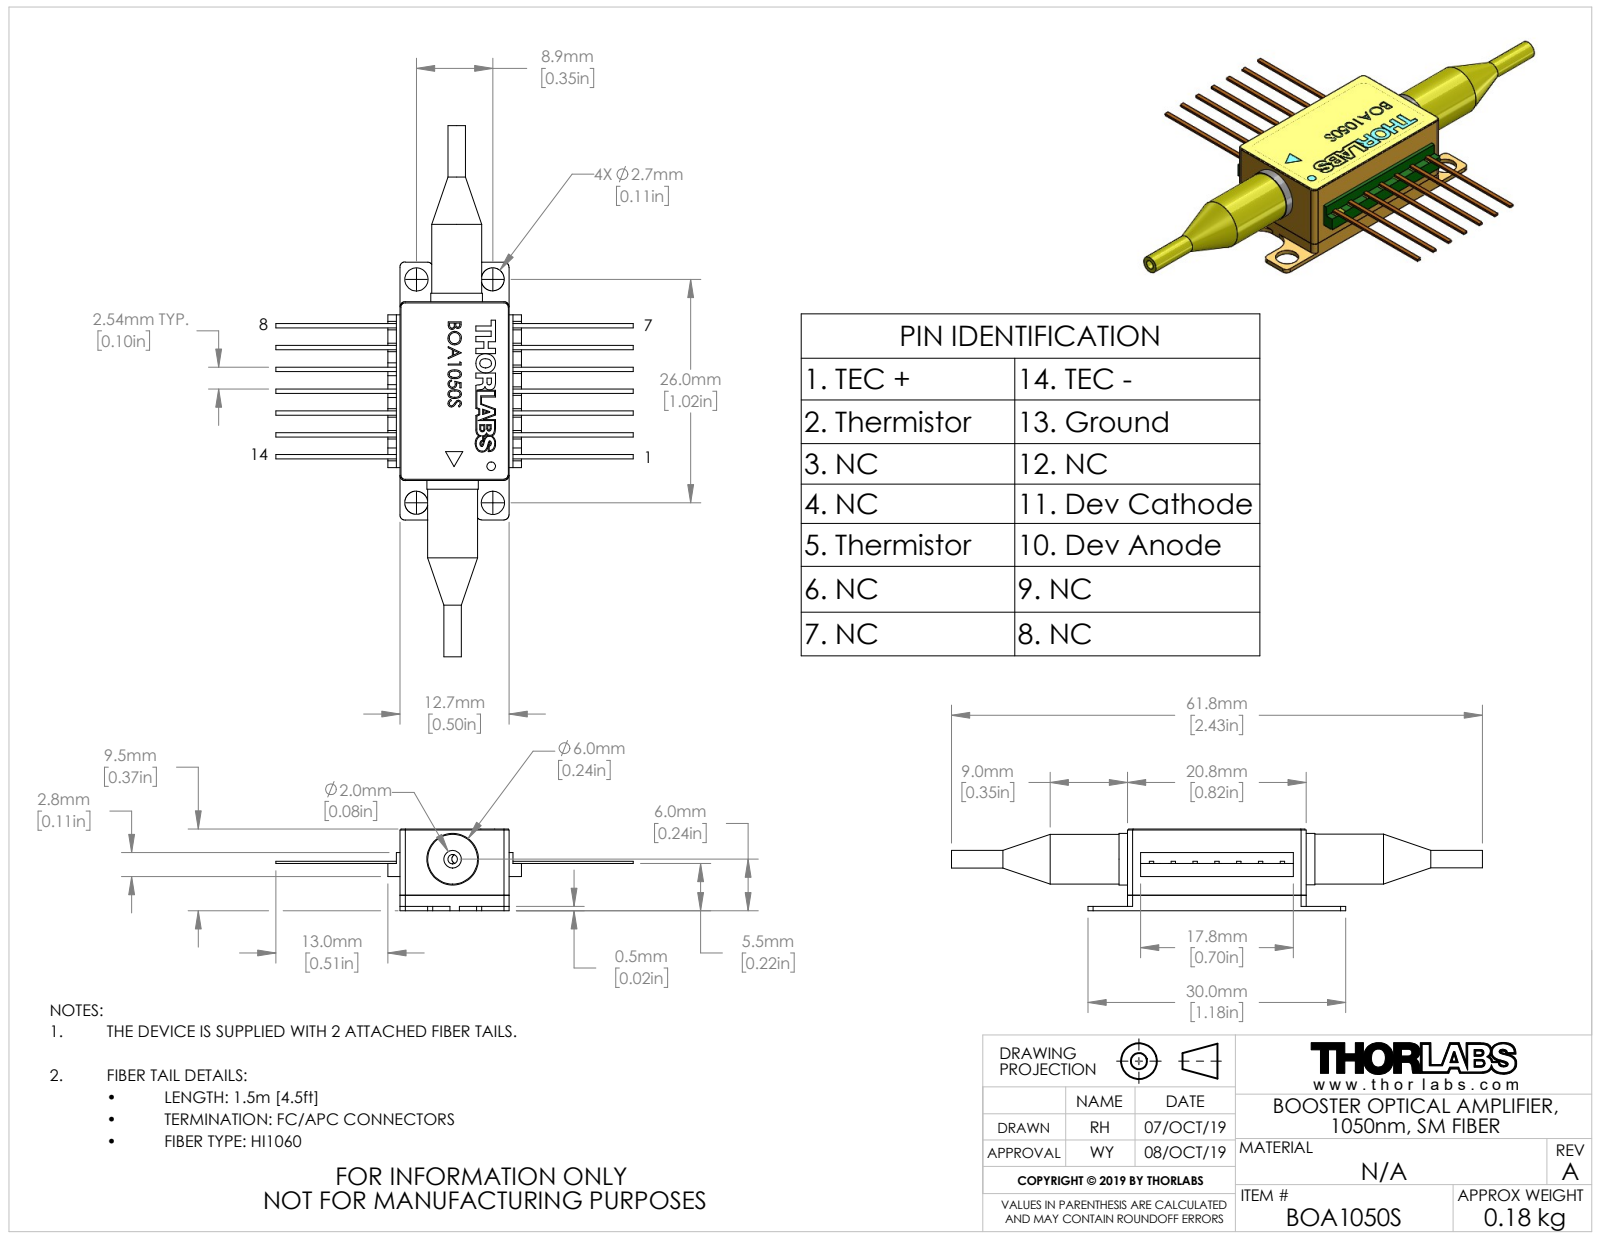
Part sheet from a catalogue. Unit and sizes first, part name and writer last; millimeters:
Units: millimetres
Overall size (bounding box): 61.8 × 41.6 × 9.5
Round holes (diameter × count): ⌀2.7 ×4, ⌀1.1 ×2, ⌀1 ×1
Round bosses / shafts (diameter × count): ⌀6 ×2, ⌀5.8 ×2, ⌀2.04 ×2
Partial cylindrical surfaces — rounded edges, fillets, slot ends (radius × count): R0.6 ×12, R0.5 ×4, R2 ×4
Main face-to-face distances: 9.5, 12.7, 1.8, 7.7, 1.52, 5.49, 3.69, 4.01, 2.17, 3.97
Hole centre spacings: 8.9, 26, 27.48, 0.47, 4.26, 9.69, 21.74, 23.42
Bodies: 0 solids, 388 faces (264 planar, 50 cylindrical, 74 other)
Part name (STEP PRODUCT): QTN037704-E0W
STEP written by: SolidWorks 2018 (AUTOMOTIVE_DESIGN)
